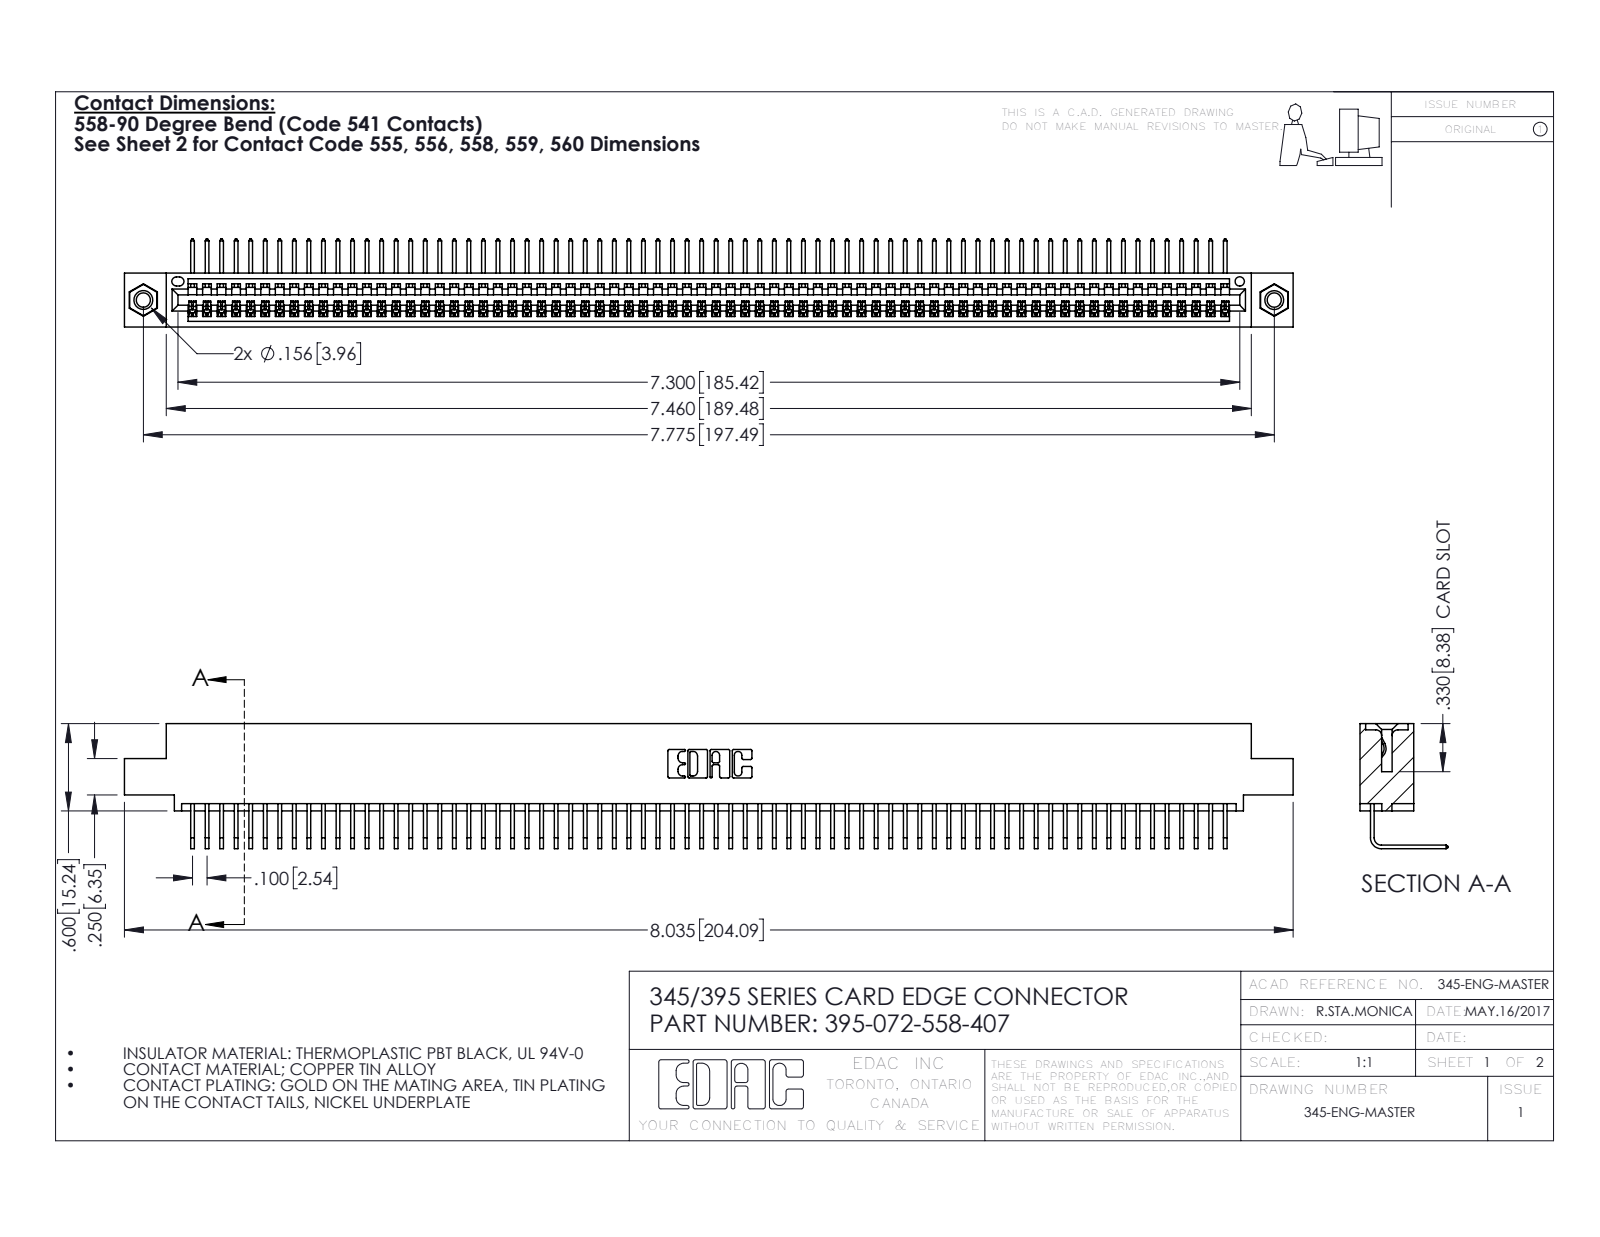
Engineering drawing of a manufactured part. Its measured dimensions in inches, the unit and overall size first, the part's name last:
Units: inches
Overall size (bounding box): 8.035 × 0.859 × 0.605
Round holes (diameter × count): ⌀0.098 ×2, ⌀0.125 ×2, ⌀0.156 ×2, ⌀0.064 ×1
Round bosses / shafts (diameter × count): ⌀0.155 ×2
Partial cylindrical surfaces — rounded edges, fillets, slot ends (radius × count): R0.006 ×144, R0.01 ×22, R0.007 ×6, R0.031 ×6, R0.026 ×3, R0.031 ×2, R0.04 ×2, R0.014 ×1
Main face-to-face distances: 0.072, 0.298, 0.37, 0.2, 0.098, 0.272, 0.025, 0.225, 0.149, 0.072
Hole centre spacings: 0.27, 7.539, 7.775
Volume: 1.207 in³ · Surface area: 43.74 in²
Bodies: 75 solids, 4510 faces (3140 planar, 1354 cylindrical, 16 other)
Part name (STEP PRODUCT): 345-292-001_558 Tail - 2; 395-072-558-407; 345 Part_0.110 Offset - 0.156 Dia-TI; 345-250-001_345-250-005-103
STEP written by: SolidWorks 2016 (CONFIG_CONTROL_DESIGN)
